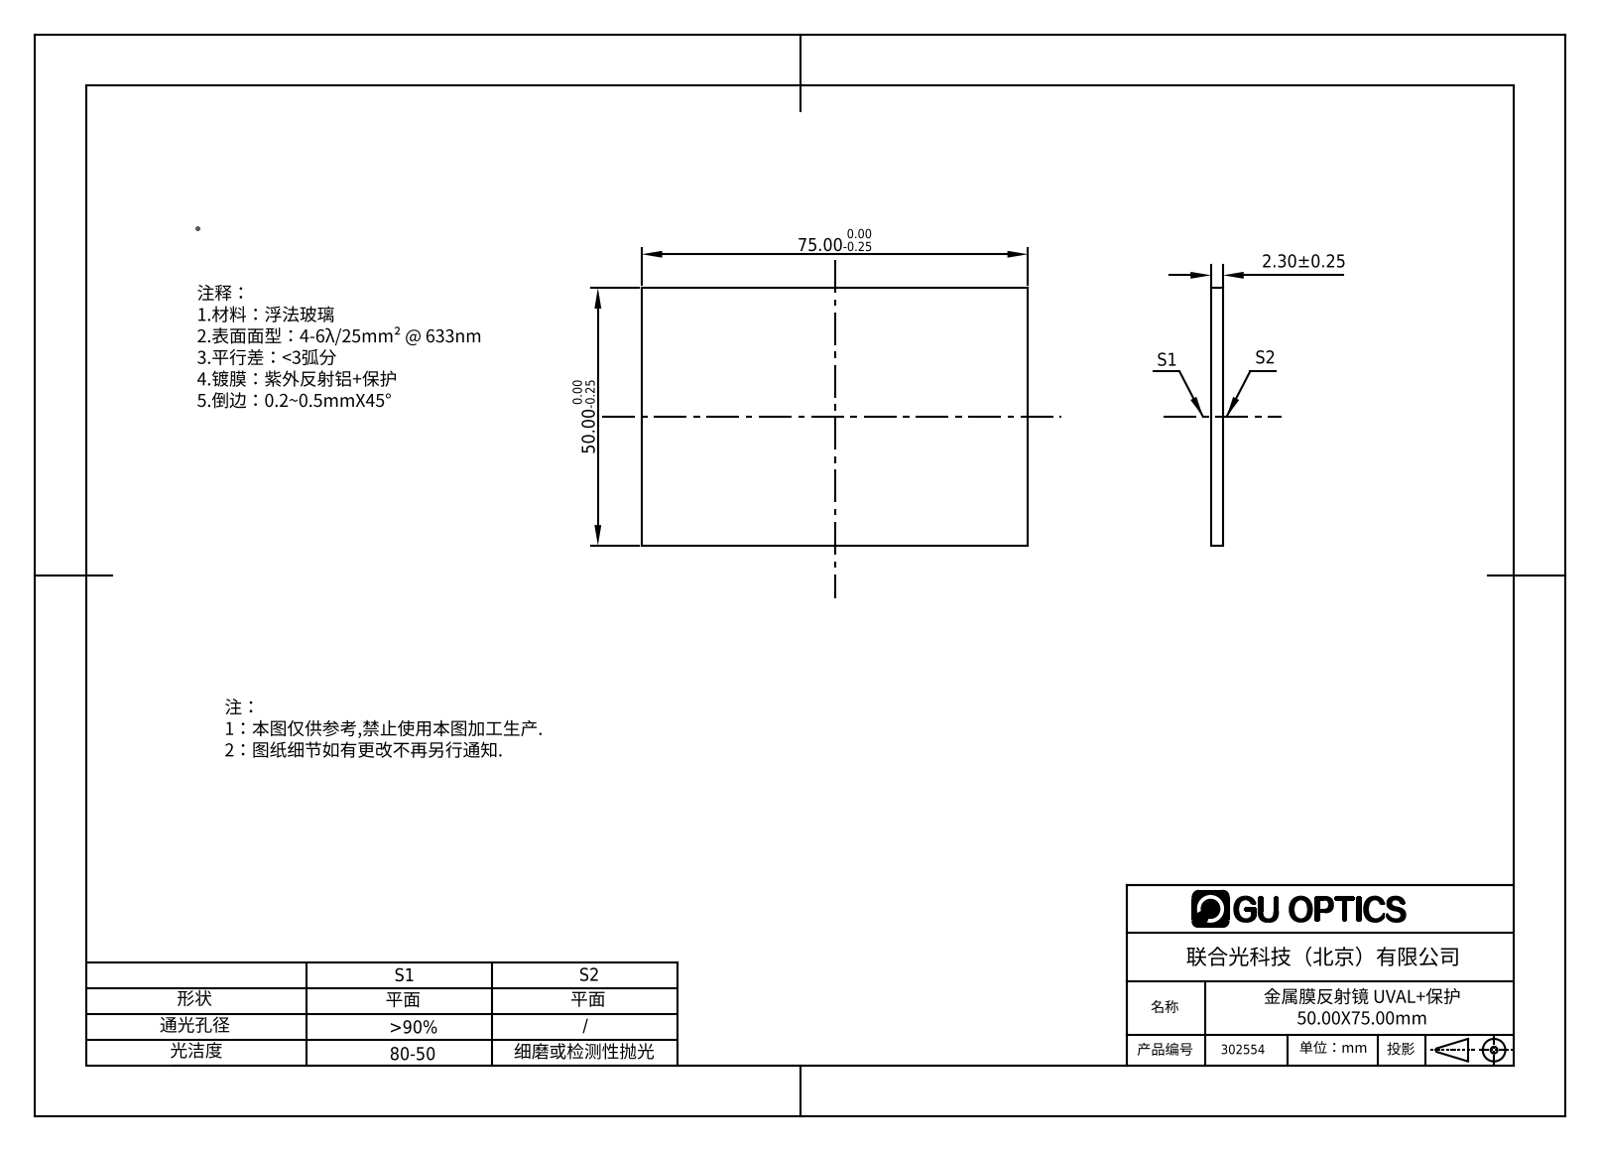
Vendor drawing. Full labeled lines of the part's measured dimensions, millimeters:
Part name (STEP PRODUCT): 302525
STEP written by: SolidWorks 2016 (AUTOMOTIVE_DESIGN)
Units: millimetres
Bodies: 1 solid, 6 faces (6 planar, 0 cylindrical, 0 other)
Overall size (bounding box): 75 × 50 × 2.3
Volume: 8 625 mm³ · Surface area: 8 075 mm²
Main face-to-face distances: 2.3, 50, 75
